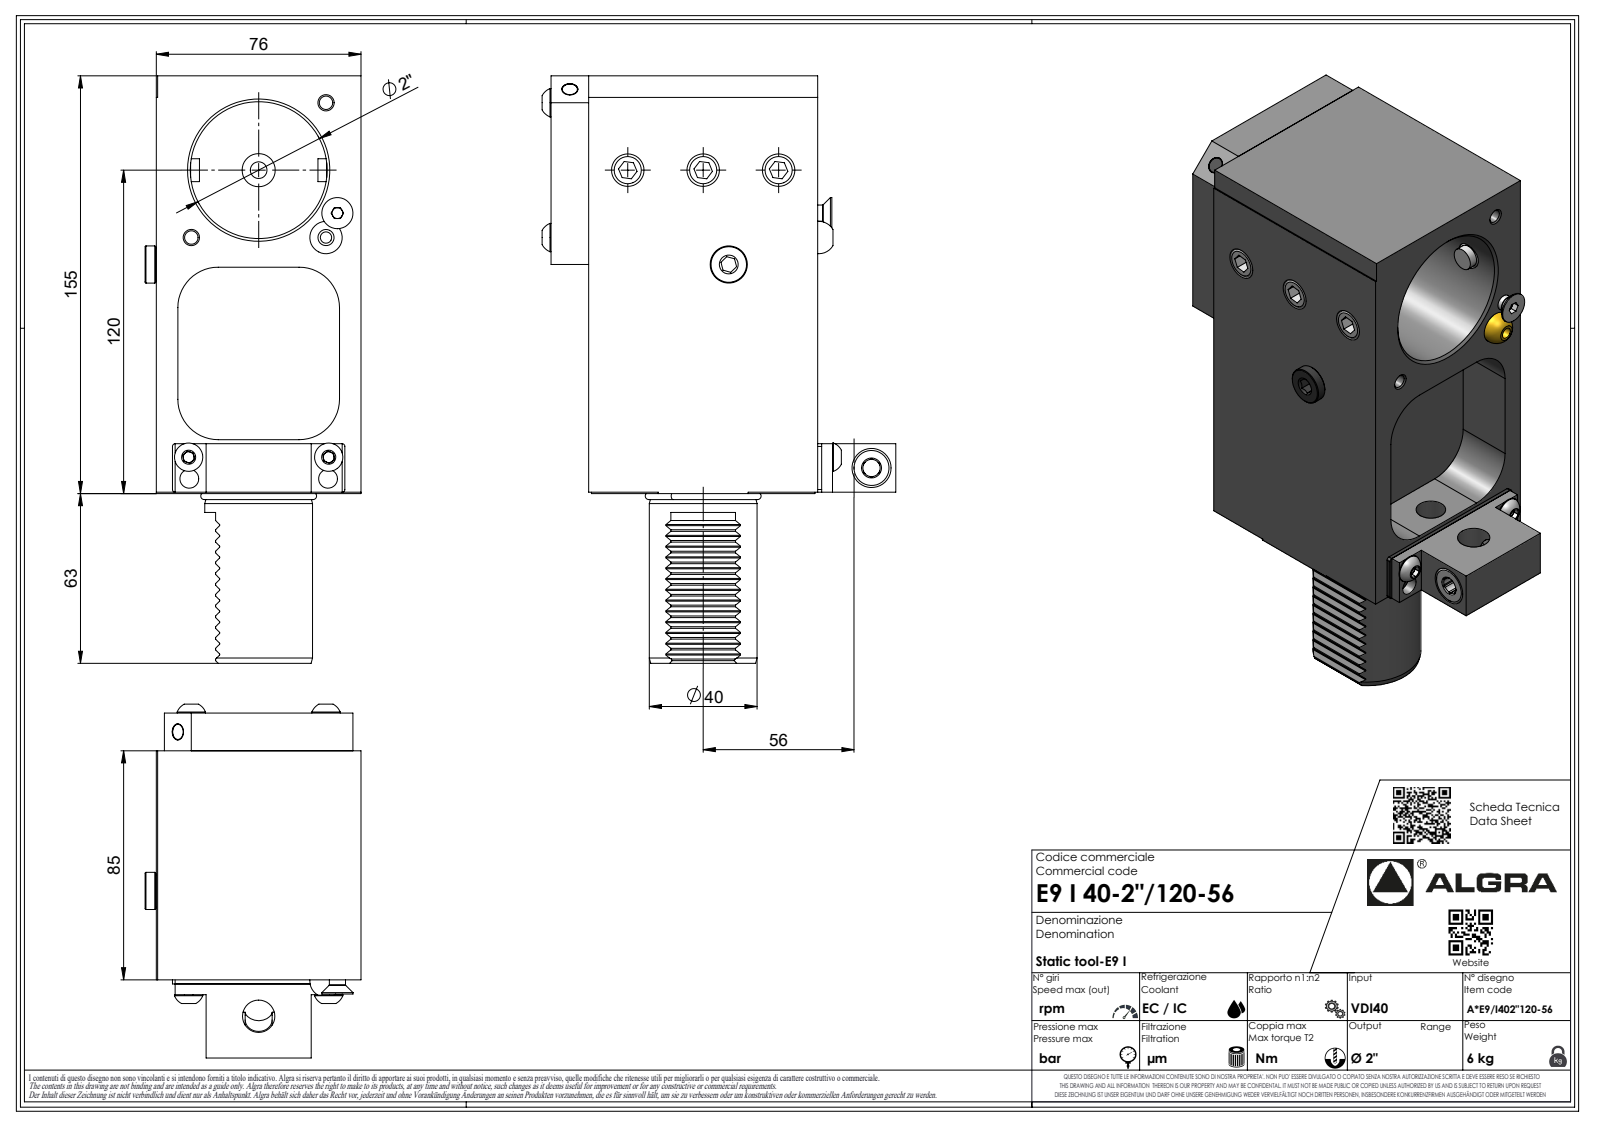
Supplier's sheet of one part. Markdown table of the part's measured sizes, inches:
| quantity | value |
| --- | --- |
| part name | E9I40-2120-56 |
| STEP written by | SolidWorks 2023 (AUTOMOTIVE_DESIGN) |
| units | inches |
| bodies | 1 solid, 403 faces (276 planar, 58 cylindrical, 69 other) |
| overall size | 8.583 × 5.039 × 3.156 |
| volume | 50.86 in³ |
| surface area | 158.5 in² |
| round holes (diameter × count) | 0.083 × 1, 2 × 1 |
| round bosses / shafts (diameter × count) | 1.575 × 1, 1.524 × 1, 0.543 × 1, 0.472 × 1, 0.251 × 1, 0.067 × 1 |
| partial cylindrical surfaces (radius × count) | 0.012 × 13, 0.013 × 7, 0.02 × 7, 0.146 × 7, 0.039 × 4, 0.591 × 4, 0.008 × 1, 1.634 × 1 |
| main face-to-face distances | 2.992, 2.48, 0.866, 3.346, 0.551, 3.898, 6.102, 1.614, 3.031, 1.417 |
